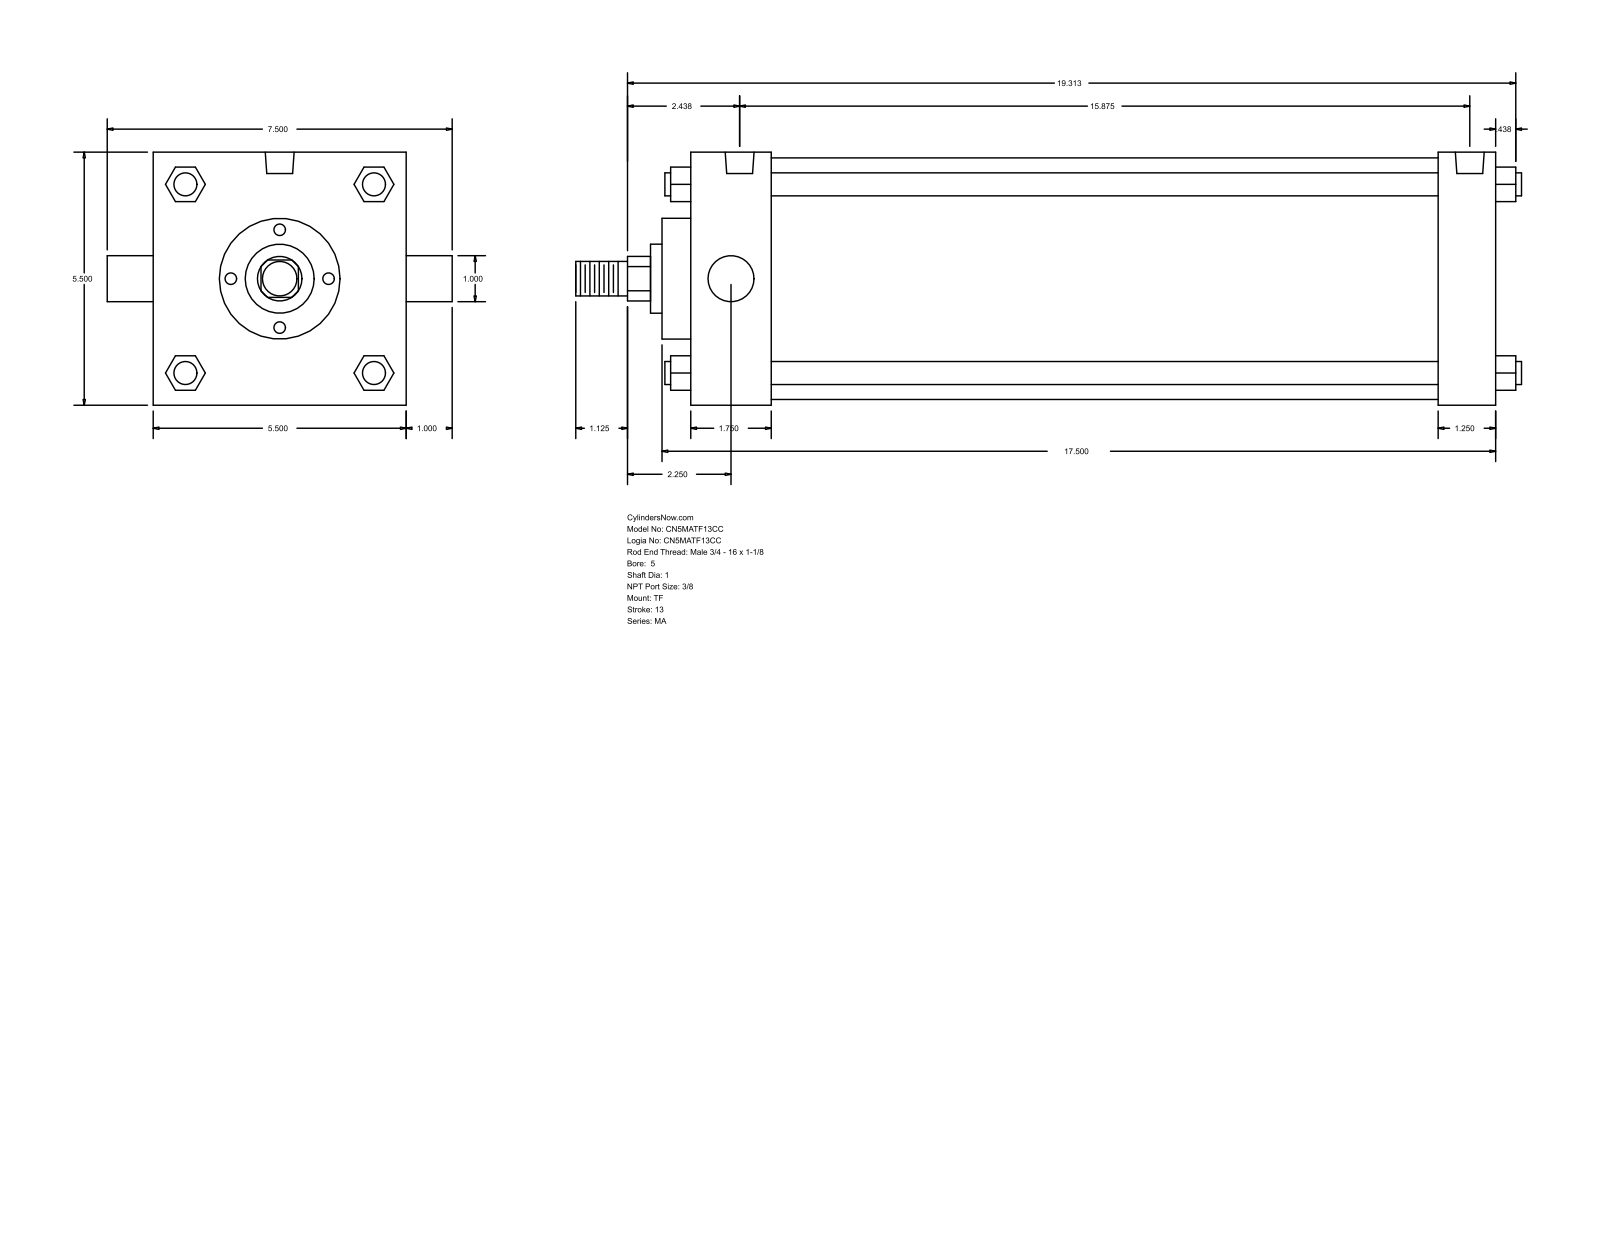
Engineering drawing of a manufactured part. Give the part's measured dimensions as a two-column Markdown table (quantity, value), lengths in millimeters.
| quantity | value |
| --- | --- |
| part name | MA_TF__0500_1 |
| STEP written by | GSSL Pune (CONFIG_CONTROL_DESIGN) |
| units | millimeters |
| bodies | 0 solids, 122 faces (93 planar, 29 cylindrical, 0 other) |
| overall size | 522.29 × 190.5 × 139.7 |
| round holes (diameter × count) | 11.11 × 3, 15.93 × 2 |
| round bosses / shafts (diameter × count) | 12.7 × 4, 25.4 × 2, 133.35 × 1, 66.67 × 1, 38.1 × 1, 19.05 × 1 |
| partial cylindrical surfaces (radius × count) | 12.29 × 1 |
| main face-to-face distances | 139.7, 444.51, 412.76, 31.75, 44.46, 368.3, 400.05, 15.87, 60.33, 428.63 |
| hole center spacings | 4.76, 398.47, 393.71, 403.23 |
